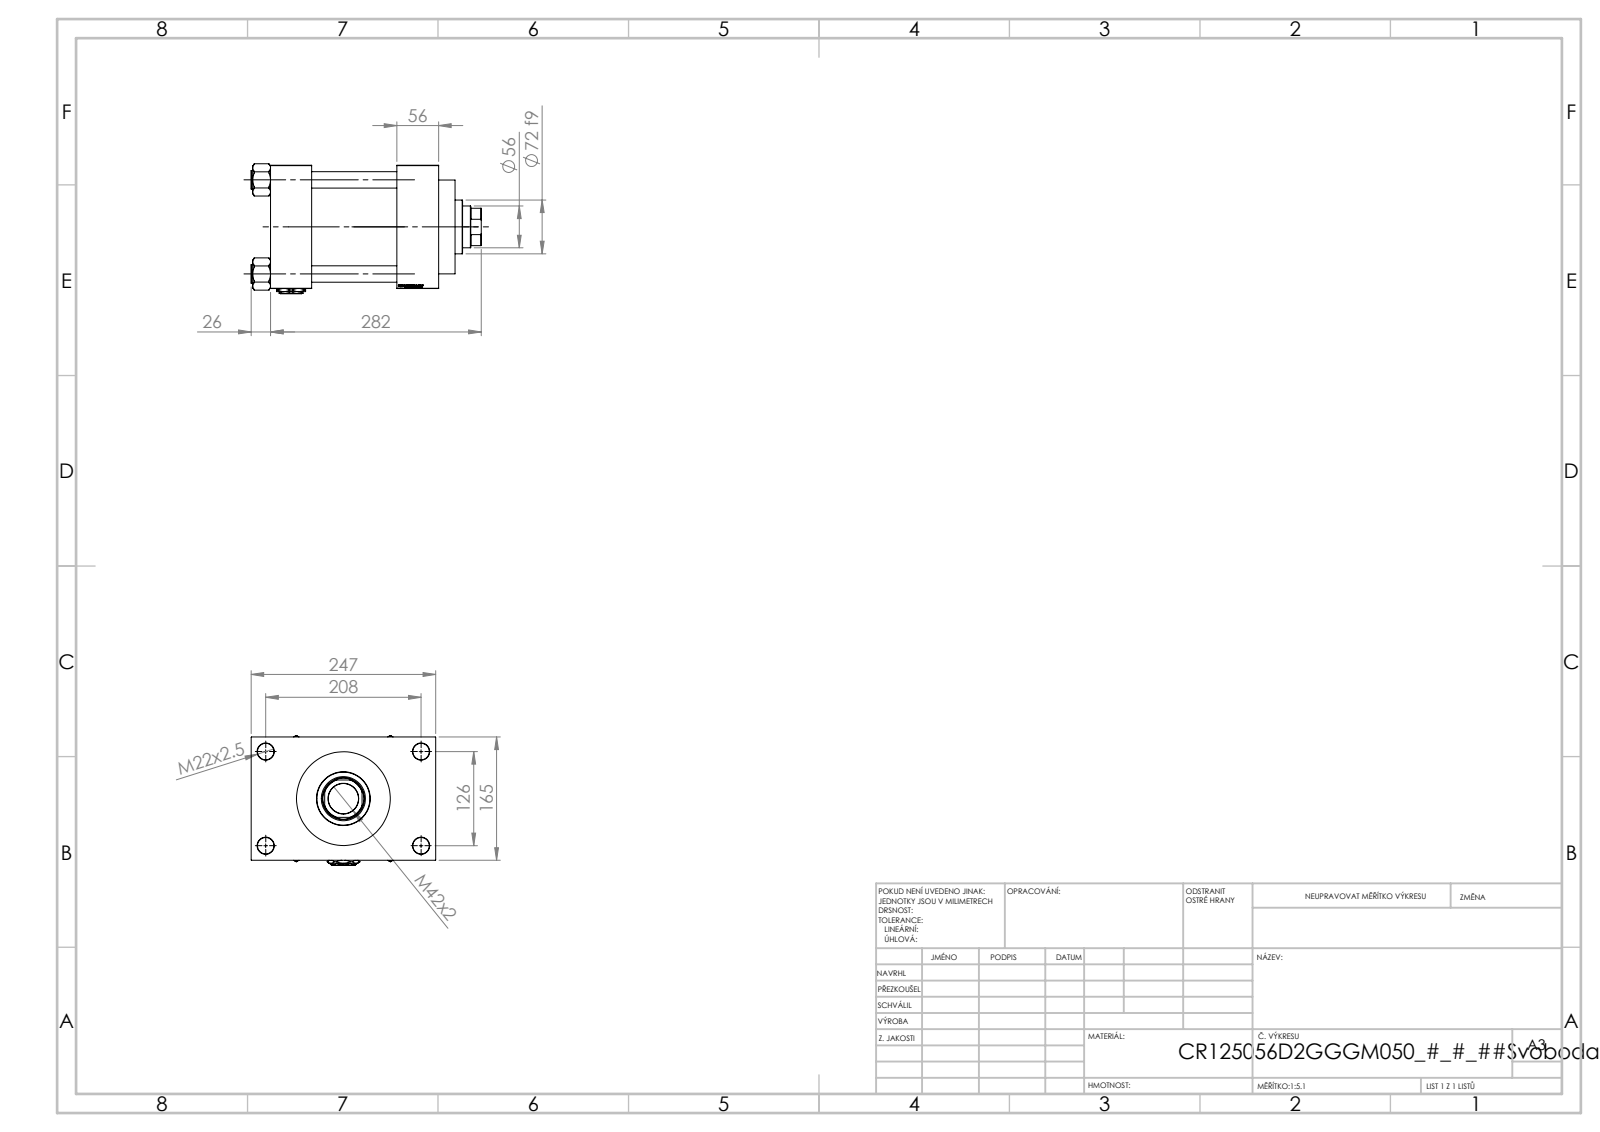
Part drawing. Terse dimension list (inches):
name: V215CR_D_TYCINKA; V215CR_D_Body; V215_VC_A; V215CR_VCP_D (+2 more)
written by: SolidWorks 2019 (CONFIG_CONTROL_DESIGN)
unit: in
bodies: 12 solids, 1202 faces (568 planar, 94 cylindrical, 540 other)
size: 12.126 × 9.724 × 6.853
volume: 311.8 in³; area: 888.9 in²
holes: 8× ⌀0.866, 2× ⌀0.276, 2× ⌀1.269, 2× ⌀1.772, 1× ⌀1.594, 1× ⌀2.205, 1× ⌀2.323, 1× ⌀3.78, 1× ⌀4.921, 1× ⌀4.941
bosses: 4× ⌀0.984, 1× ⌀5.157, 1× ⌀2.835
rounds: 1× R1.063
face distances: 4.488, 6.496, 6.654, 2.165, 6.693, 2.205, 8.858, 1.614, 8.11, 9.724
hole spacings: 1.616, 3.505, 4.787, 4.957, 5.215, 6.573, 8.233, 4.961
